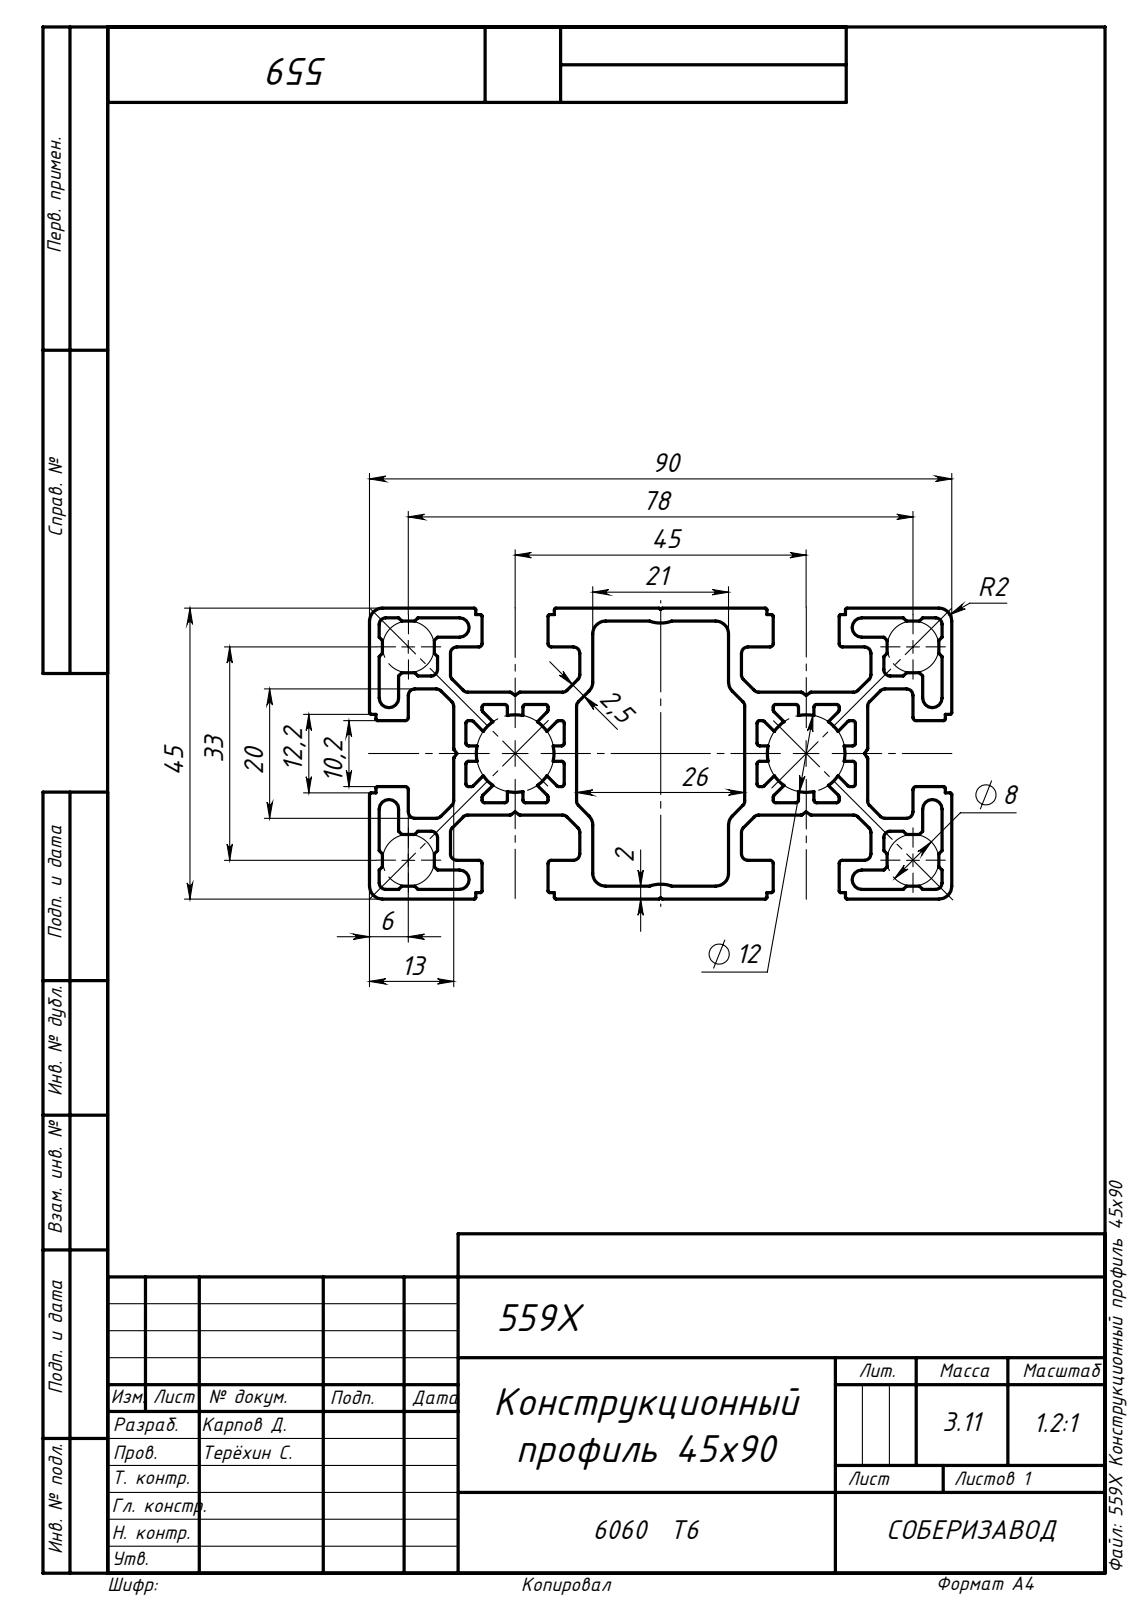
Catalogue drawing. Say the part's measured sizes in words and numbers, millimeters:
The part is named "559X Конструкционный профиль 45х90". Its 3-D file was written by "SolidWorks 2019 (AUTOMOTIVE_DESIGN)". It is 1 solid with 458 faces: 272 planar, 186 cylindrical and 0 other. Overall it measures 1000 by 90 by 45 millimeters. Its volume is 1 150 000 cubic millimeters and its surface area 1 031 000 square millimeters. Partial cylindrical surfaces (rounded edges, fillets, slot ends): 48 of radius 0.4, 48 of radius 1, 36 of radius 0.25, 12 of radius 0.5, 12 of radius 2, 8 of radius 1.5, 2 of radius 5, 2 of radius 6. The main face-to-face distances are 45, 1.5, 2.5, 32, 13, 30.5, 4.5, 0.5, 11.5, 4.4.
